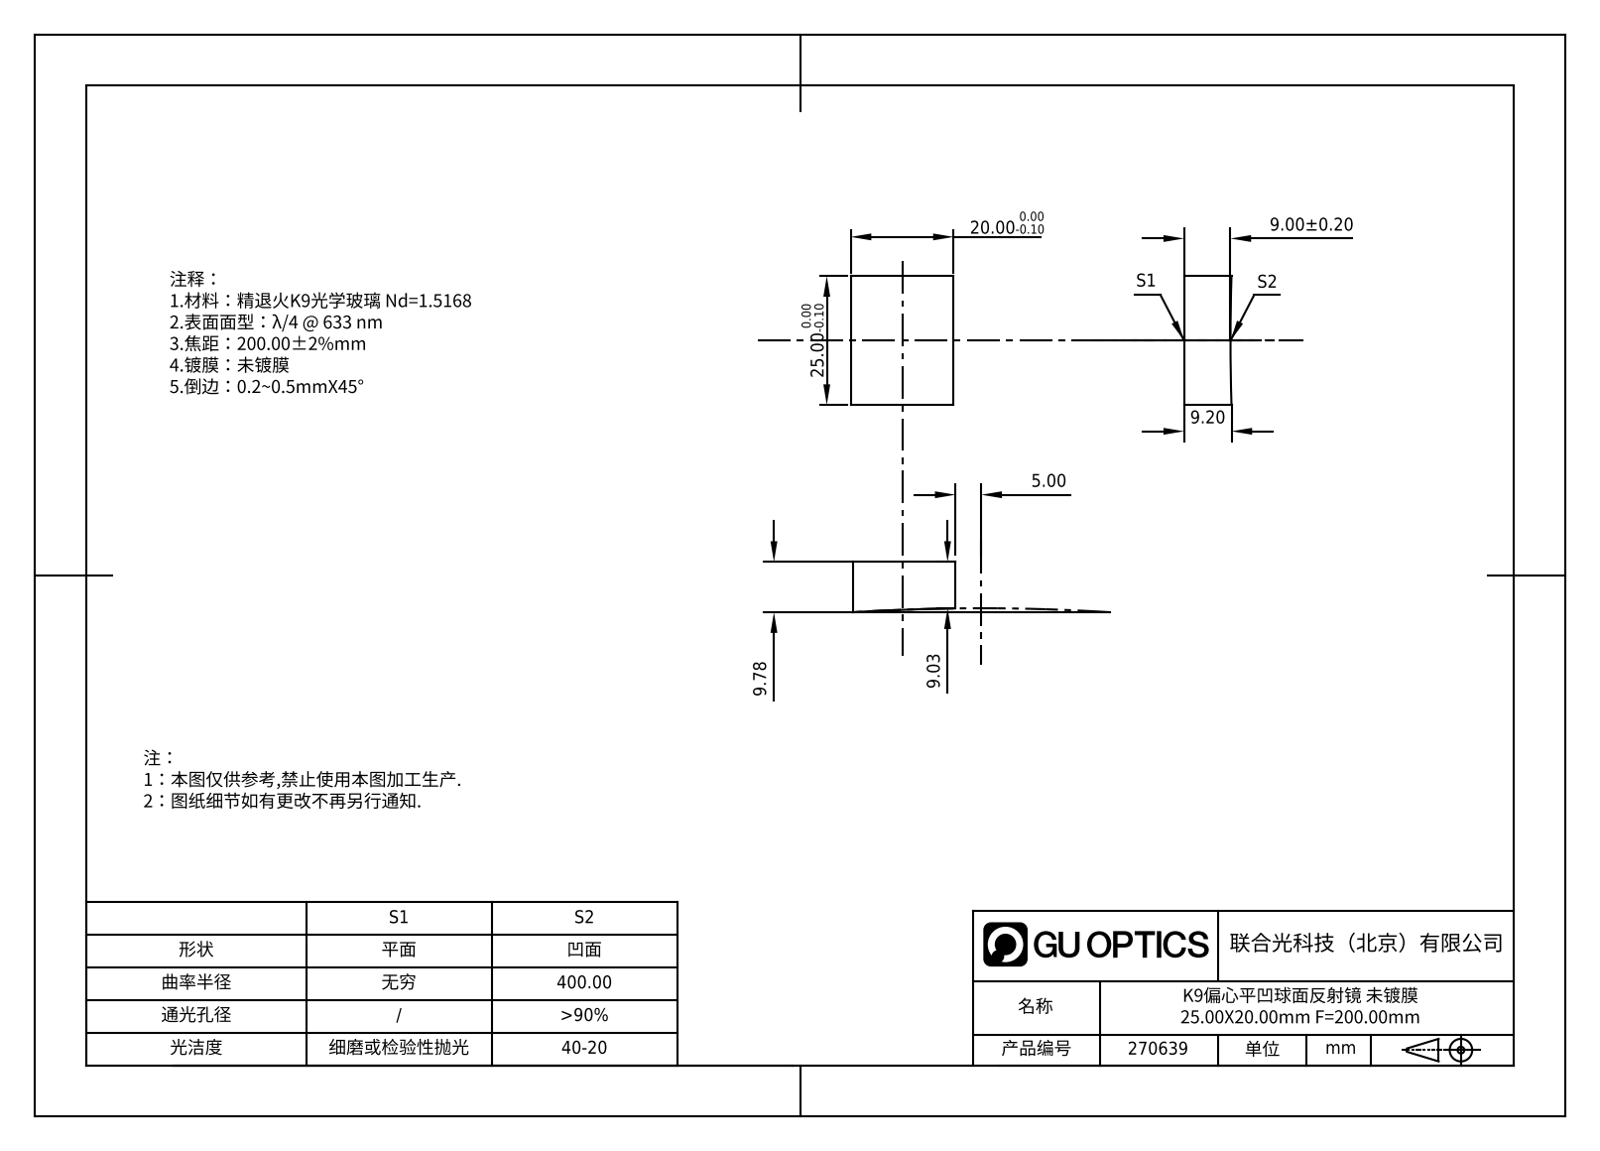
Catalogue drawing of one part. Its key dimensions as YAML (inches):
part_name: "270639"
step_written_by: "SolidWorks 2020 (CONFIG_CONTROL_DESIGN)"
units: inches
bodies: {solids: 1, faces: 7, planar: 5, cylindrical: 0, other: 2}
overall_size: [0.984, 0.787, 0.393]
volume: 0.286
surface_area: 2.875
face_to_face_distances: [0.787, 0.984]
